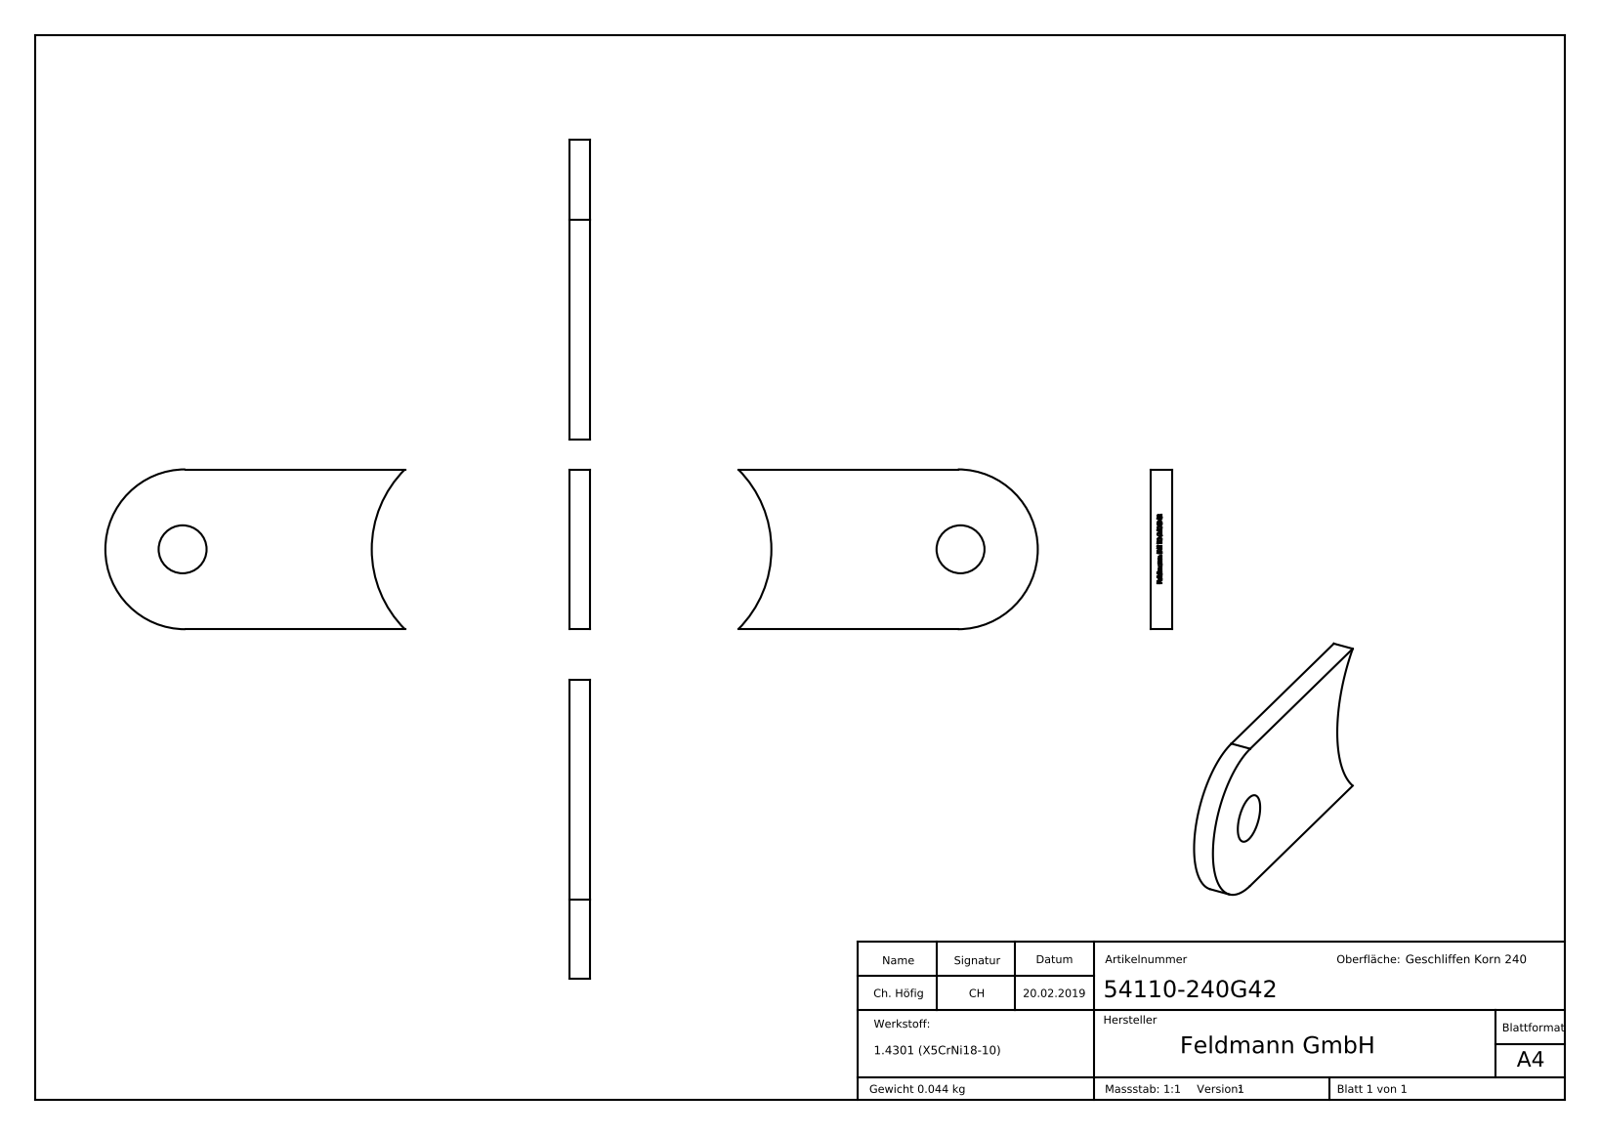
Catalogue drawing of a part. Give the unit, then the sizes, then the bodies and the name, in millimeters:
Units: millimetres
Overall size (bounding box): 56.22 × 30 × 4
Round holes (diameter × count): ⌀9 ×1
Partial cylindrical surfaces — rounded edges, fillets, slot ends (radius × count): R15 ×1, R21.2 ×1, R21.3 ×1
Main face-to-face distances: 4, 30, 2, 0.61, 2.18, 0.53, 1.21, 2.26, 2.82, 1.29
Volume: 5 591 mm³ · Surface area: 3 567 mm²
Bodies: 1 solid, 263 faces (135 planar, 33 cylindrical, 95 other)
Part name (STEP PRODUCT): 54110-240G42
STEP written by: SolidWorks 2015 (CONFIG_CONTROL_DESIGN)
